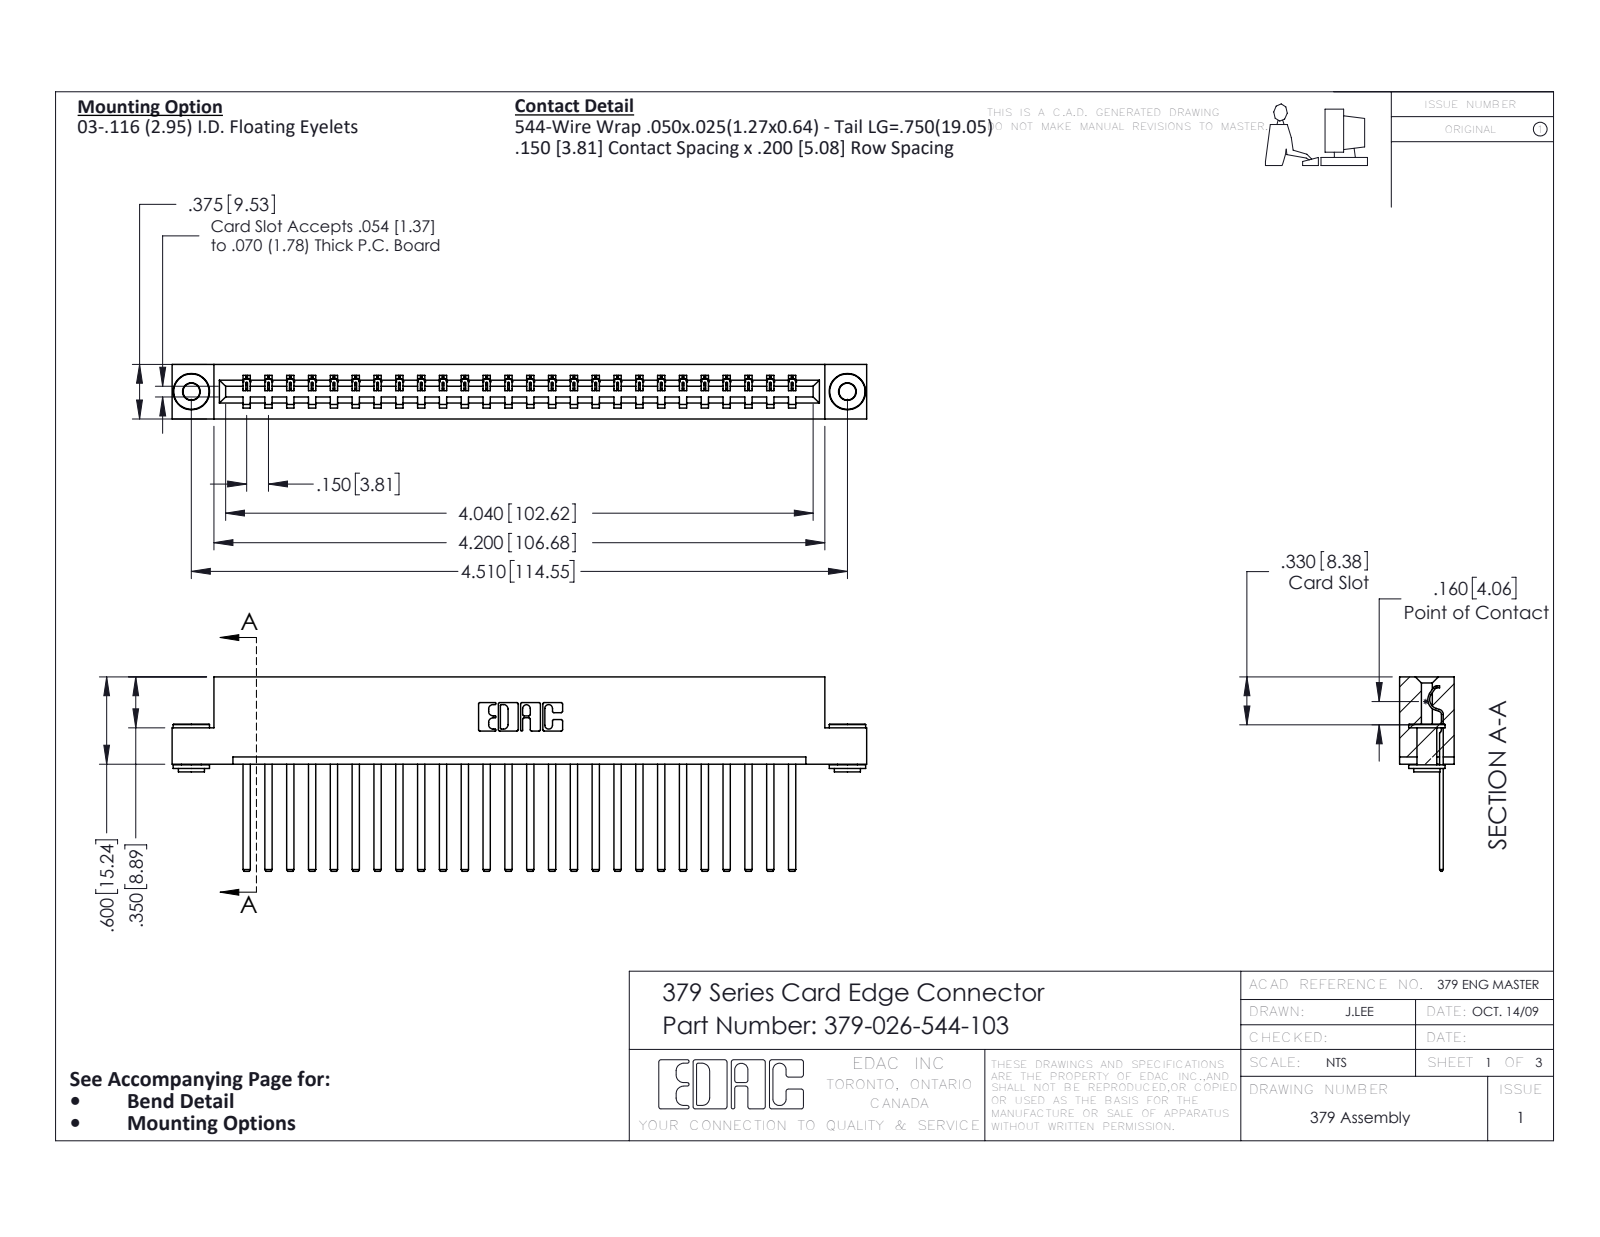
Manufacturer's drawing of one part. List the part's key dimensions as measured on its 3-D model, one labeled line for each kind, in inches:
Part name (STEP PRODUCT): 379 Part_Flush - .156 Dia - TH; 345-292-001_345-293-144; 345-250-002_345-250-002-102; 379-026-544-103
STEP written by: SolidWorks 2016 (CONFIG_CONTROL_DESIGN)
Units: inches
Bodies: 29 solids, 1504 faces (1068 planar, 428 cylindrical, 8 other)
Overall size (bounding box): 4.775 × 1.337 × 0.375
Volume: 0.786 in³ · Surface area: 22.19 in²
Round holes (diameter × count): ⌀0.116 ×2, ⌀0.156 ×2
Round bosses / shafts (diameter × count): ⌀0.25 ×2, ⌀0.18 ×2, ⌀0.136 ×2
Partial cylindrical surfaces — rounded edges, fillets, slot ends (radius × count): R0.006 ×52, R0.01 ×22, R0.007 ×6, R0.031 ×6, R0.026 ×3, R0.014 ×1, R0.022 ×1, R0.024 ×1
Main face-to-face distances: 0.3, 0.075, 0.375, 0.275, 0.025, 0.1, 0.6, 0.225, 0.2, 0.15
Hole centre spacings: 4.51
